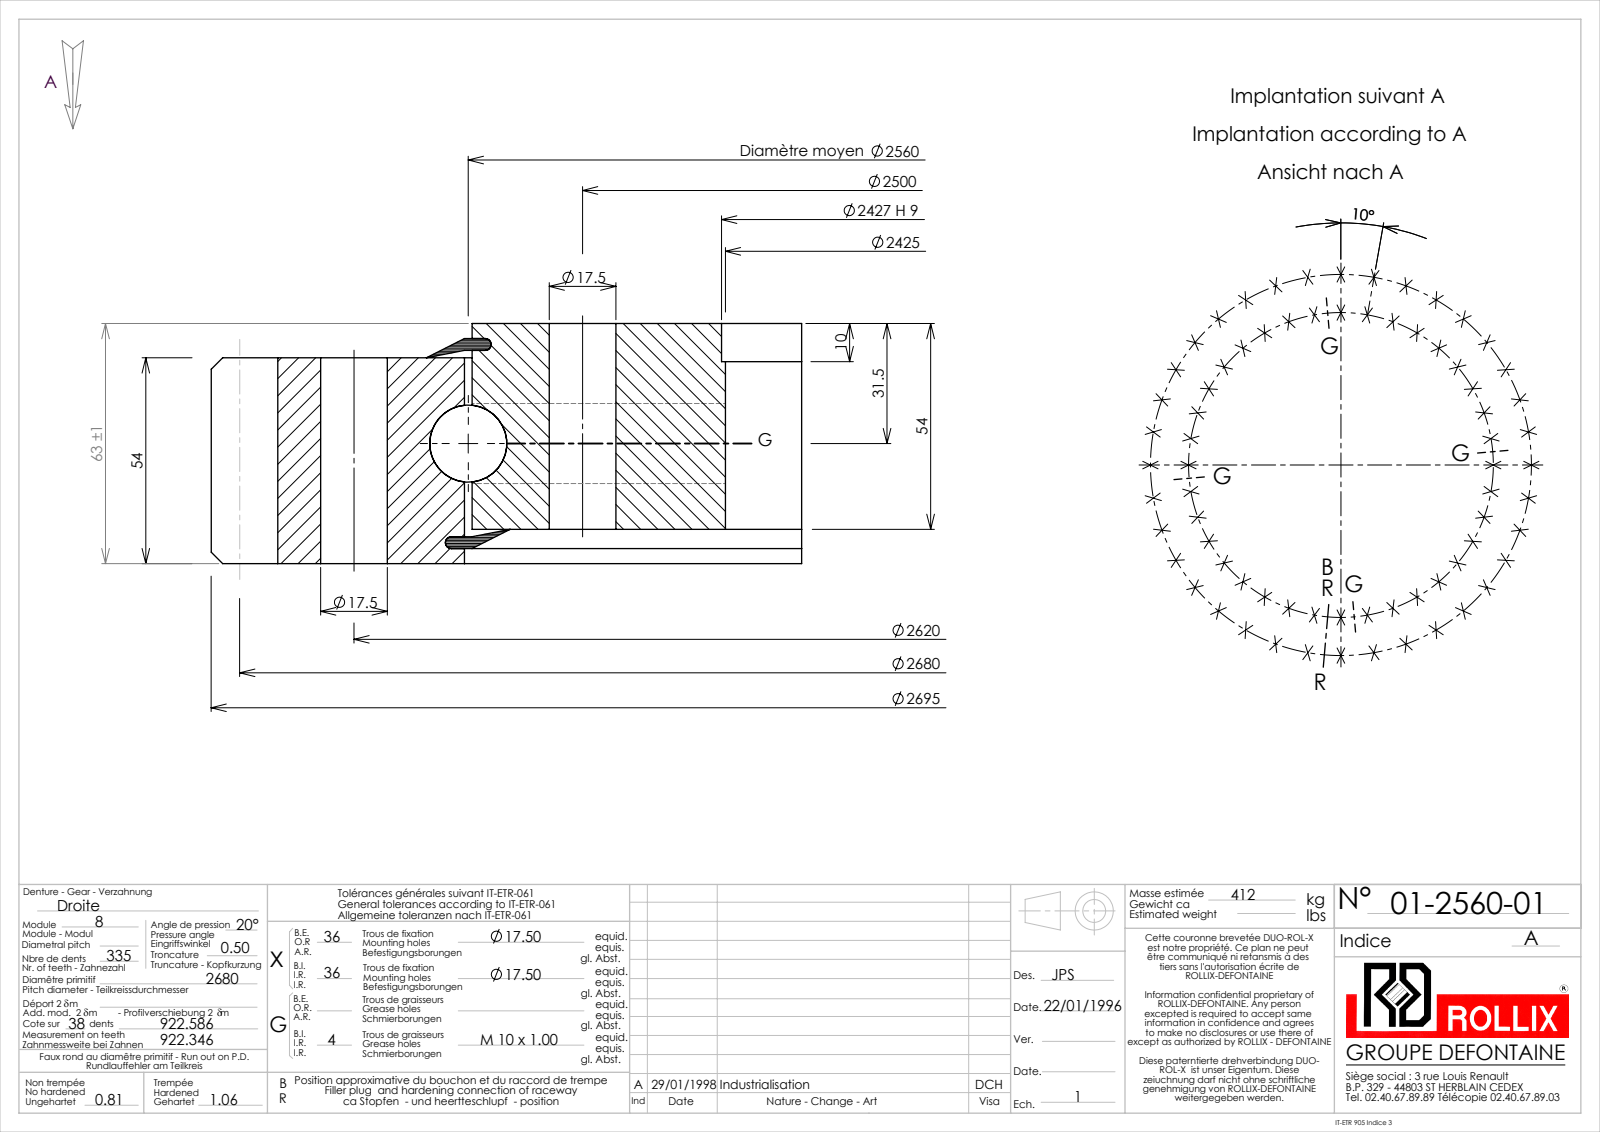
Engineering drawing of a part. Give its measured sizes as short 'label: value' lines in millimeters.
name: 01-2560-01
written by: SolidWorks 2016 (CONFIG_CONTROL_DESIGN)
unit: mm
bodies: 5 solids, 2221 faces (683 planar, 839 cylindrical, 699 other)
size: 2694.99 × 2694.97 × 63
volume: 51 100 000 mm³; area: 5 247 000 mm²
holes: 72× ⌀17.5, 4× ⌀9, 1× ⌀2425, 1× ⌀2427, 1× ⌀2562.03
bosses: 1× ⌀2557.97
rounds: 1× R1330, 1× R1347.5
face distances: 54, 9, 63, 45, 3.95, 59.05, 5.05, 50.05, 7.05, 55.95
hole spacings: 1107.26, 1310, 2146.18, 228.35, 454.96, 2374.53, 2462, 2610.03
